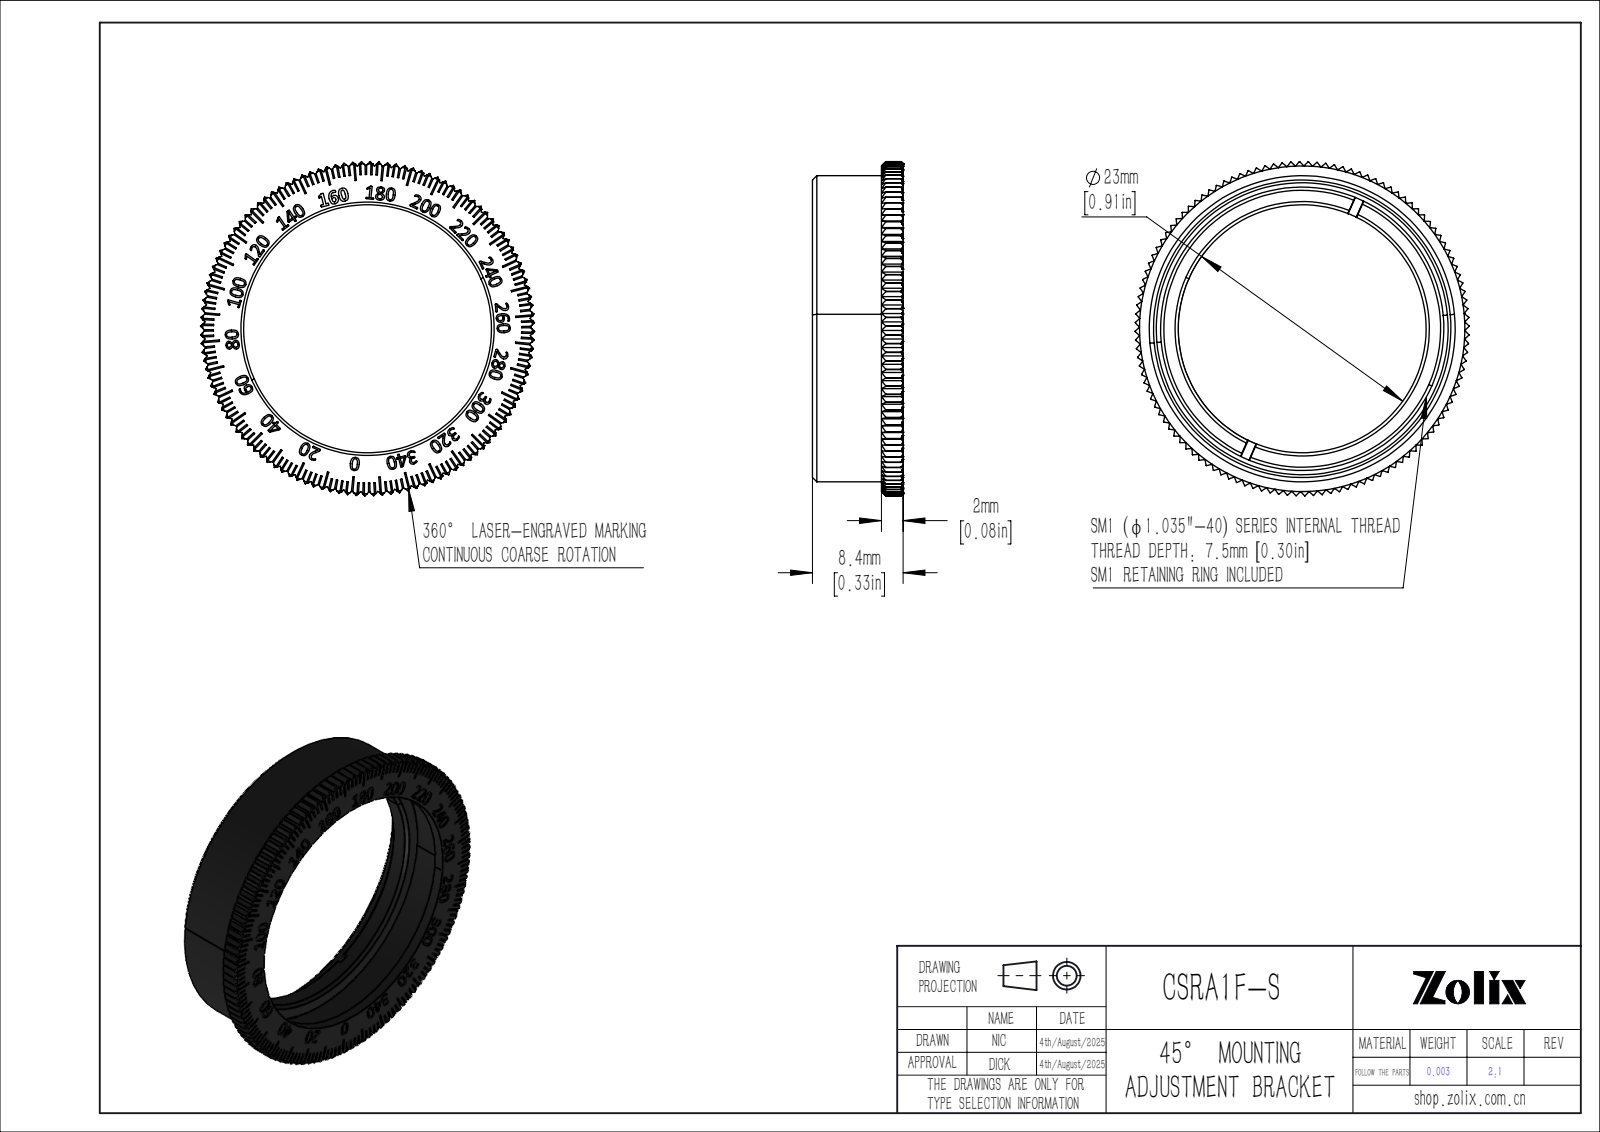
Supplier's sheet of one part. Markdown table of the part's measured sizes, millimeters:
| quantity | value |
| --- | --- |
| part name | CSRA1F-S |
| STEP written by | SolidWorks 2020 (CONFIG_CONTROL_DESIGN) |
| units | millimeters |
| bodies | 2 solids, 1448 faces (1056 planar, 136 cylindrical, 256 other) |
| overall size | 31 × 26.52 × 26.52 |
| volume | 1 261 mm³ |
| surface area | 2 732 mm² |
| round holes (diameter × count) | 23 × 1, 23.5 × 1, 26.29 × 1, 27.5 × 1 |
| round bosses / shafts (diameter × count) | 28.4 × 1 |
| partial cylindrical surfaces (radius × count) | 15.5 × 1 |
| main face-to-face distances | 0.99, 1, 1.99, 2.45, 3.45, 4.44, 2.05, 4.5, 5.5, 6.49 |
